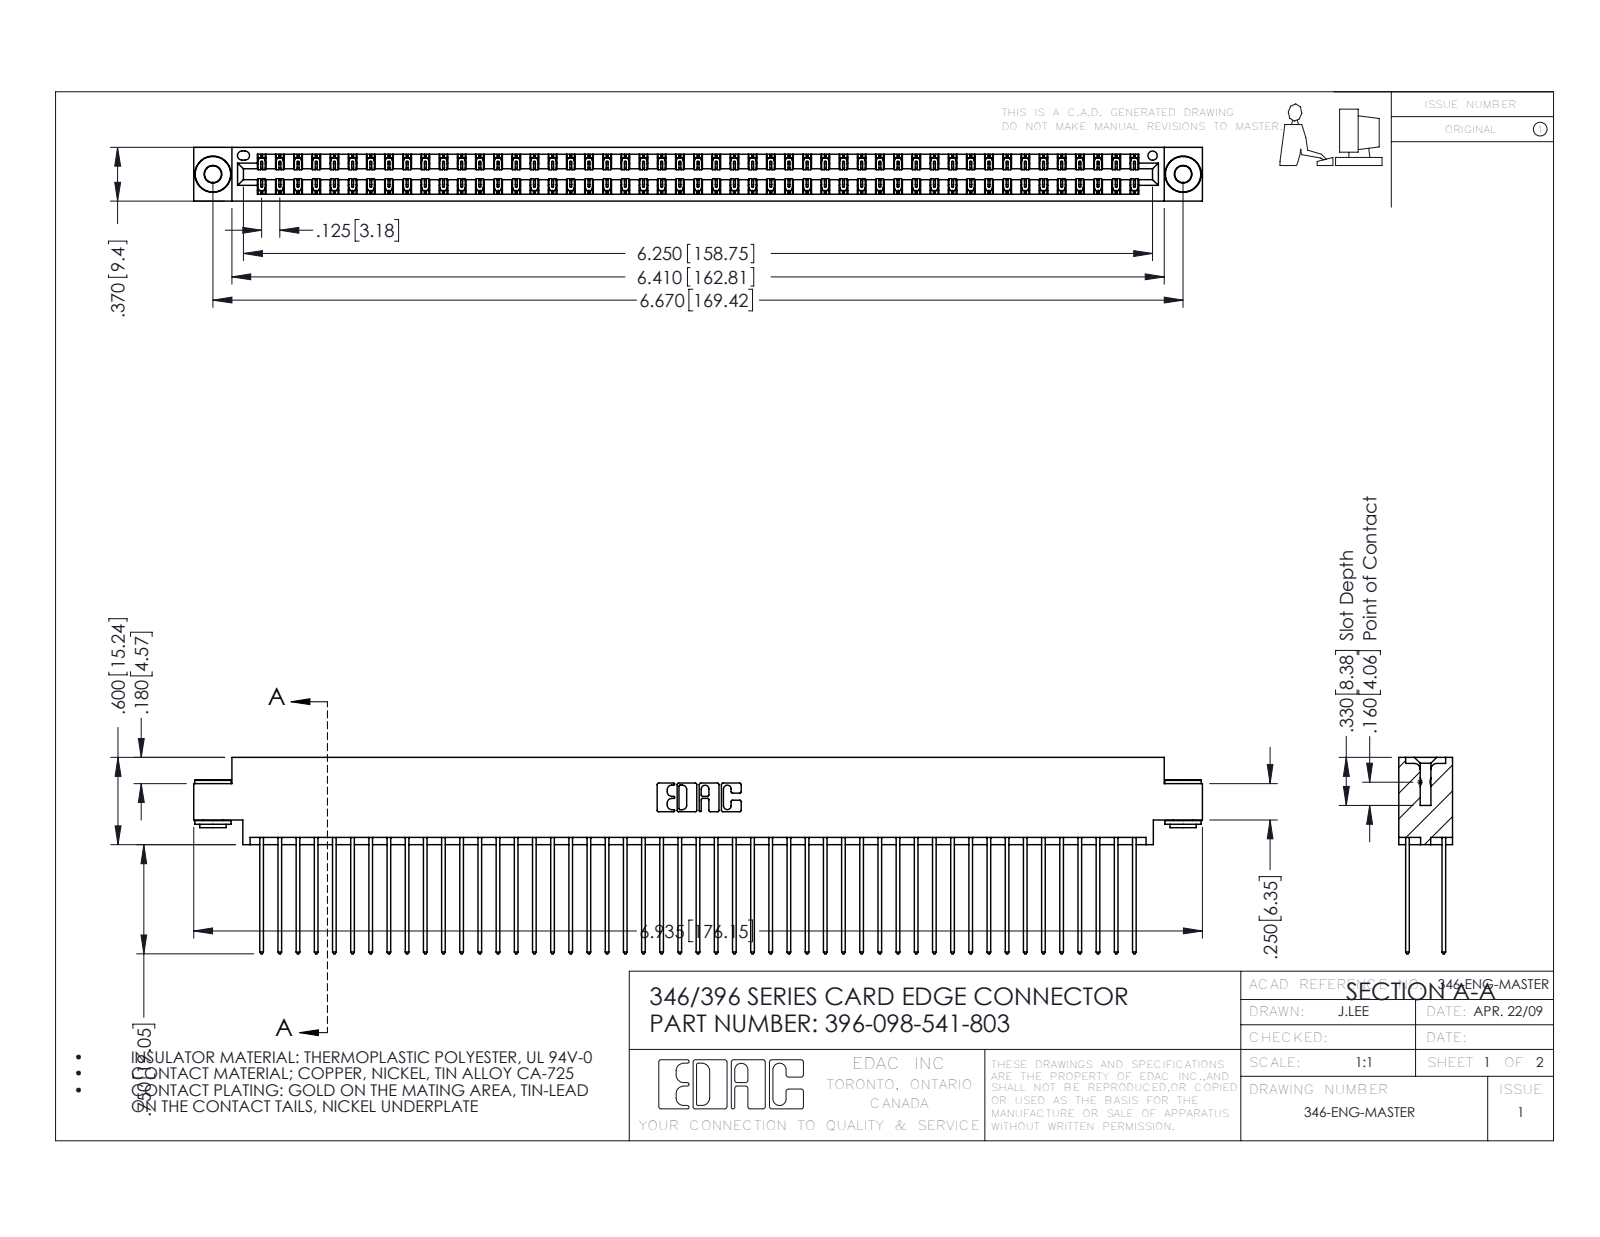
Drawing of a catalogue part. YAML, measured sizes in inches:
part_name: "346 Part_0.170 Offset - 0.156 Dia-TH; 345-292-001_345-293-141; 396-098-541-803; 345-250-002_345-250-002-102"
step_written_by: "SolidWorks 2016 (CONFIG_CONTROL_DESIGN)"
units: inches
bodies: {solids: 101, faces: 5260, planar: 3520, cylindrical: 1732, other: 8}
overall_size: [6.935, 1.35, 0.37]
volume: 1.078
surface_area: 42.58
round_holes:
  - {diameter: 0.116, count: 2}
  - {diameter: 0.156, count: 2}
  - {diameter: 0.064, count: 1}
round_bosses_or_shafts:
  - {diameter: 0.25, count: 2}
  - {diameter: 0.18, count: 2}
  - {diameter: 0.136, count: 2}
partial_cylinders:
  - {radius: 0.006, count: 147}
  - {radius: 0.01, count: 98}
  - {radius: 0.01, count: 22}
  - {radius: 0.007, count: 6}
  - {radius: 0.031, count: 6}
  - {radius: 0.026, count: 3}
  - {radius: 0.014, count: 2}
  - {radius: 0.022, count: 2}
face_to_face_distances: [0.048, 0.322, 0.25, 0.025, 0.072, 0.298, 0.37, 0.275, 0.225, 0.148]
hole_center_spacings: [0.246, 6.461, 6.67]
